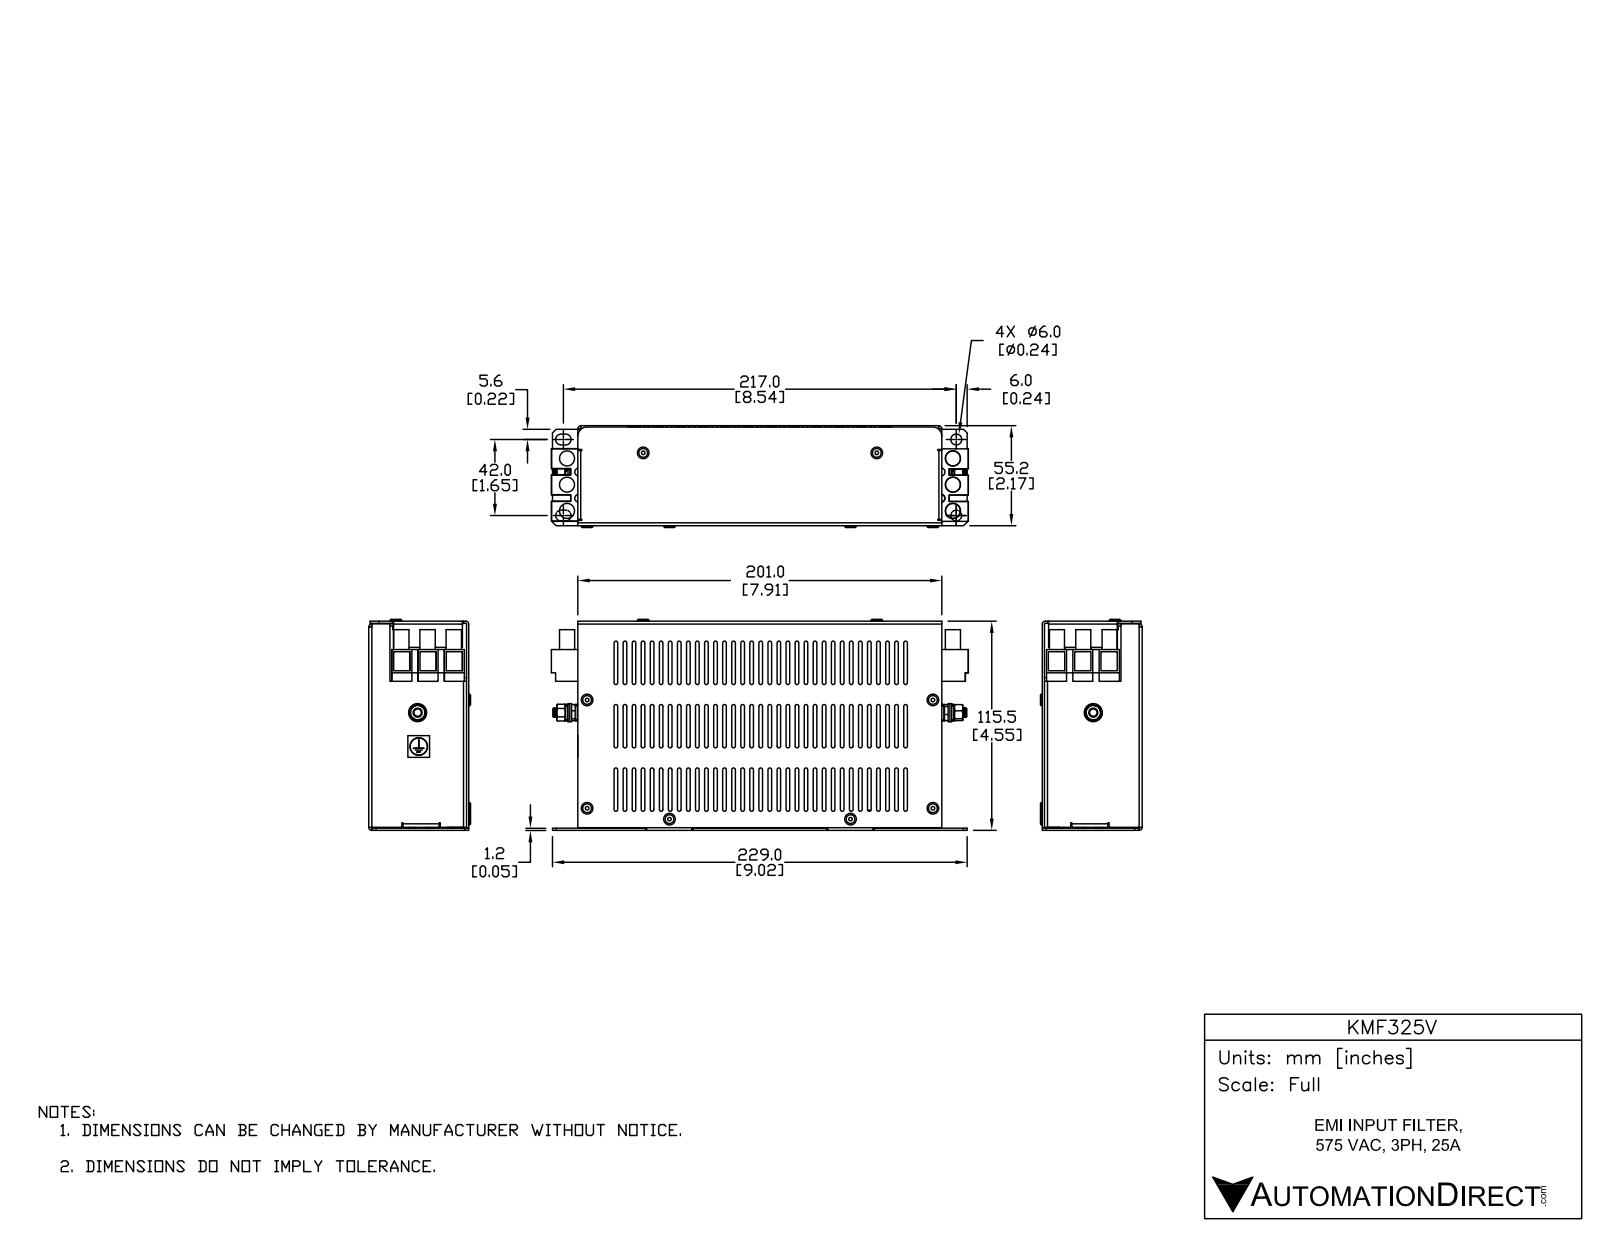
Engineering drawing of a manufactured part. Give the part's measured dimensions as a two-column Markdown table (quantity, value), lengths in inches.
| quantity | value |
| --- | --- |
| part name | KMF325V |
| STEP written by | SolidWorks 2017 (AUTOMOTIVE_DESIGN) |
| units | inches |
| bodies | 38 solids, 2428 faces (1384 planar, 704 cylindrical, 340 other) |
| overall size | 9.067 × 4.587 × 2.213 |
| volume | 10.46 in³ |
| surface area | 324.9 in² |
| round holes (diameter × count) | 0.079 × 12, 0.138 × 12, 0.13 × 8, 0.169 × 8, 0.154 × 2, 0.236 × 2, 0.051 × 1, 0.165 × 1, 0.165 × 1, 0.205 × 1, 0.383 × 1 |
| round bosses / shafts (diameter × count) | 0.327 × 24, 0.138 × 12, 0.252 × 4, 0.394 × 1, 0.373 × 1, 0.315 × 1, 0.307 × 1, 0.268 × 1 |
| partial cylindrical surfaces (radius × count) | 0.039 × 198, 0.02 × 18, 0.076 × 7, 0.067 × 6, 0.118 × 4, 0.016 × 3, 0.029 × 3, 0.063 × 3 |
| main face-to-face distances | 0.047, 2.126, 2.079, 4.5, 2.173, 4.547, 4.453, 7.866, 0.571, 0.059 |
| hole center spacings | 0.394, 2.354, 0.571, 1.224, 1.389, 1.807, 3.15, 5.733 |
